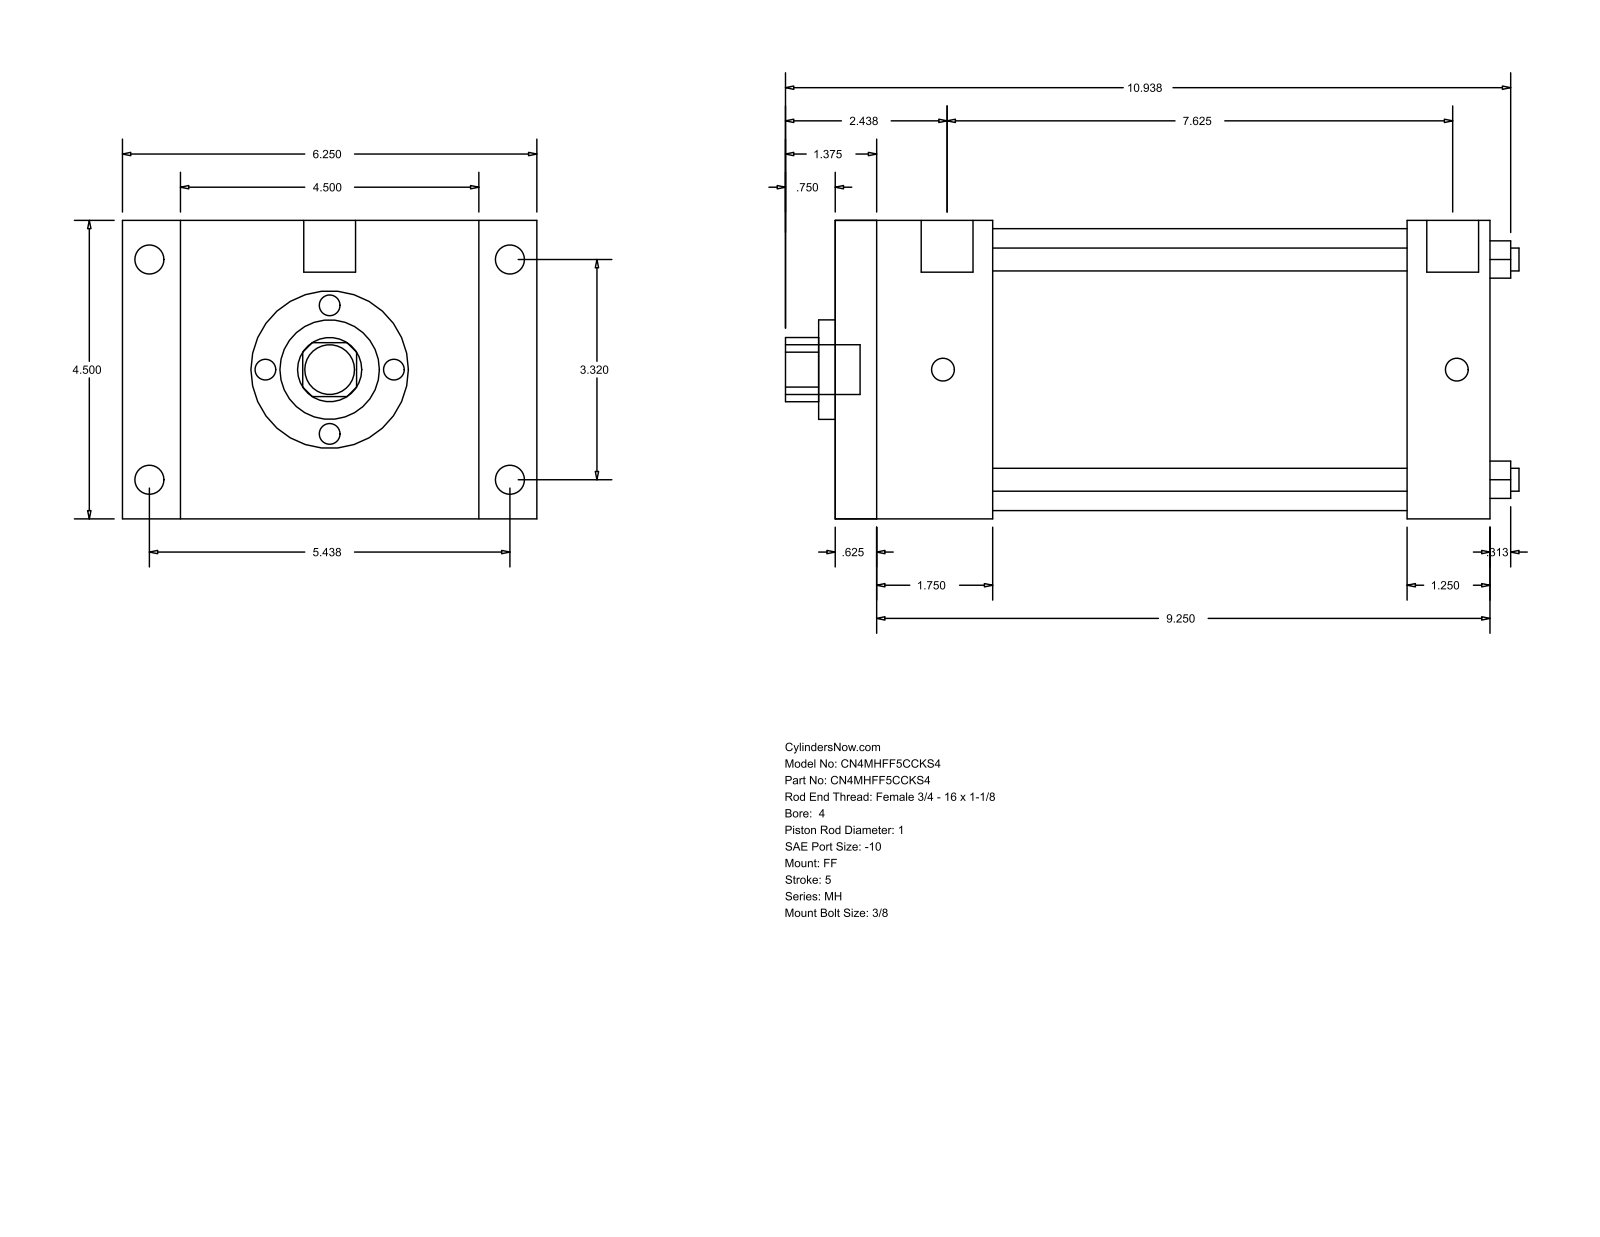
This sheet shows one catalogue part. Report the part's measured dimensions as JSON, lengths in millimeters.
{"part_name": "MH_FF__0400_1", "step_written_by": "GSSL Pune (CONFIG_CONTROL_DESIGN)", "units": "millimeters", "bodies": {"solids": 0, "faces": 92, "planar": 64, "cylindrical": 28, "other": 0}, "overall_size": [280.99, 158.75, 114.3], "round_holes": [[8.76, 4], [25.4, 1], [38.1, 1], [107.95, 1]], "round_bosses_or_shafts": [[11.13, 4], [8.73, 4], [19.84, 2], [19.05, 1]], "partial_cylinders_radius": [[12.29, 1]], "face_to_face_distances": [114.3, 250.83, 15.87, 234.96, 60.33, 44.46, 190.5, 219.07, 203.2, 158.74], "hole_center_spacings": [59.62, 84.32, 119.25]}
